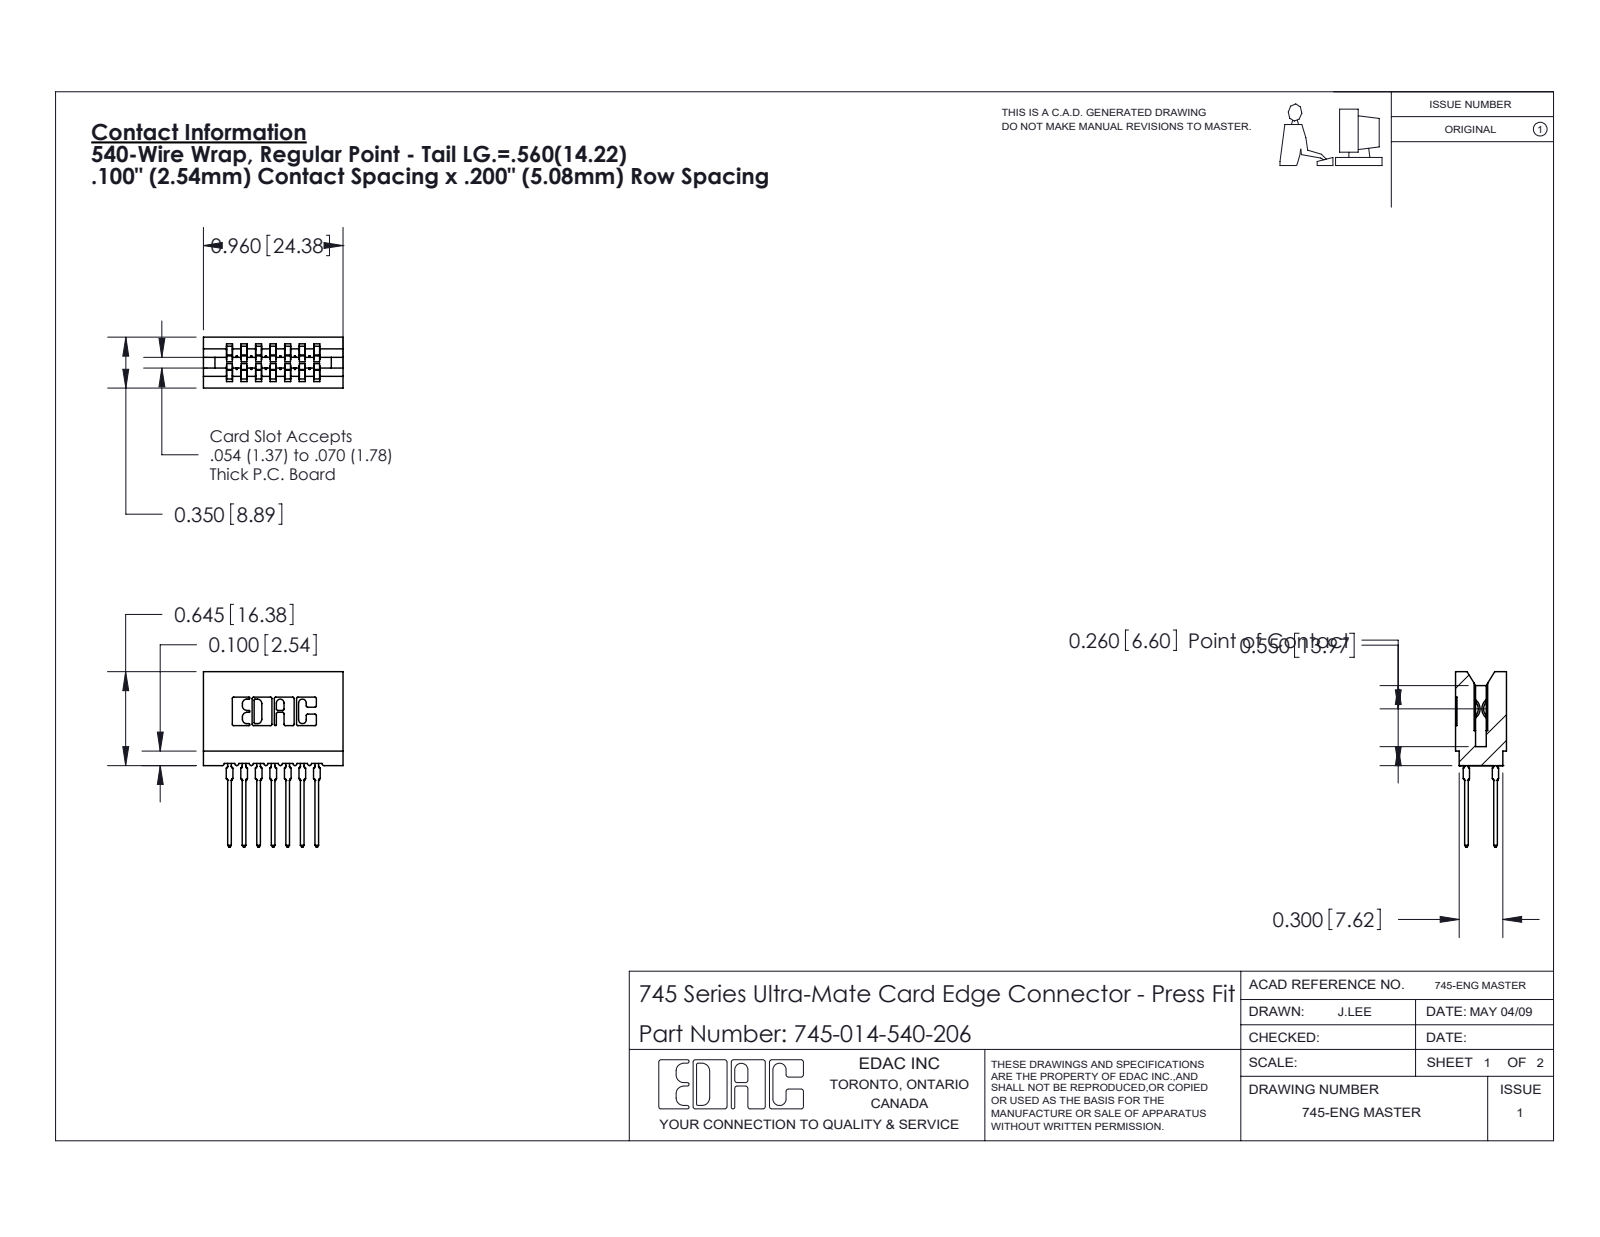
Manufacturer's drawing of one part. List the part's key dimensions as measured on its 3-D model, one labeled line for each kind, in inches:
Part name (STEP PRODUCT): 745-014-540-206; 745 Part_Insulator Option - 06; 745-292-001_540
STEP written by: SolidWorks 2020 (CONFIG_CONTROL_DESIGN)
Units: inches
Bodies: 15 solids, 1349 faces (700 planar, 285 cylindrical, 364 other)
Overall size (bounding box): 1.206 × 0.96 × 0.35
Volume: 0.148 in³ · Surface area: 6.682 in²
Partial cylindrical surfaces — rounded edges, fillets, slot ends (radius × count): R0.021 ×28, R0.01 ×22, R0.015 ×14, R0.005 ×8, R0.011 ×8, R0.007 ×6, R0.031 ×6, R0.026 ×3
Main face-to-face distances: 0.1, 0.2, 0.3, 0.042, 0.142, 0.4, 0.058, 0.242, 0.158, 0.35
